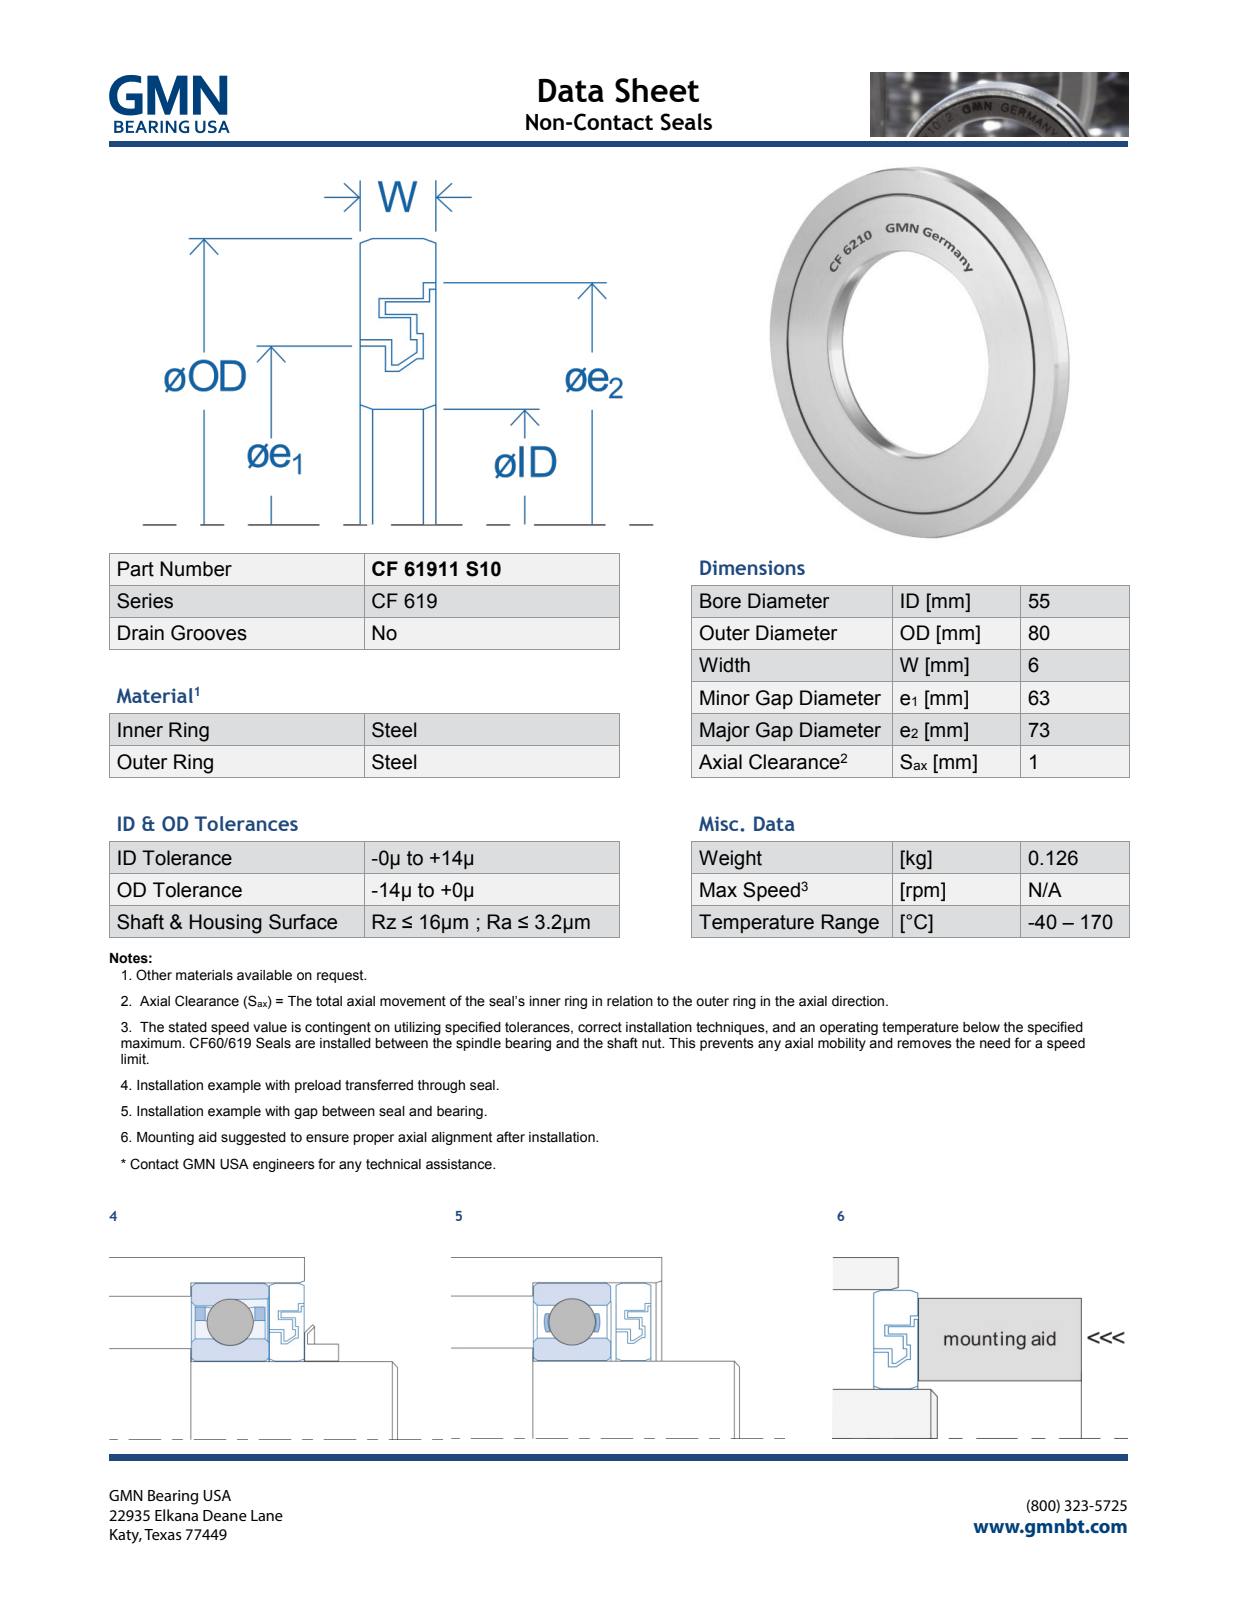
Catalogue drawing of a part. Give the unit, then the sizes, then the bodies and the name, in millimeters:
Units: millimetres
Overall size (bounding box): 80 × 80 × 6.05
Round holes (diameter × count): ⌀55 ×1, ⌀60 ×1, ⌀64 ×1, ⌀65 ×1, ⌀68 ×1, ⌀70.5 ×1, ⌀73 ×1
Round bosses / shafts (diameter × count): ⌀80 ×1, ⌀72 ×1, ⌀70 ×1, ⌀67.5 ×1, ⌀63 ×1, ⌀61 ×1, ⌀59 ×1
Main face-to-face distances: 6, 0.5, 2, 2.5, 1, 1.5, 4, 3, 3.5, 4.5
Volume: 14 056 mm³ · Surface area: 15 591 mm²
Bodies: 2 solids, 639 faces (597 planar, 30 cylindrical, 12 other)
Part name (STEP PRODUCT): CF61911S10_PRT
STEP written by: PRO/ENGINEER BY PARAMETRIC TECHNOLOGY CORPORATION, 2013150 (AUTOMOTIVE_DESIGN)
